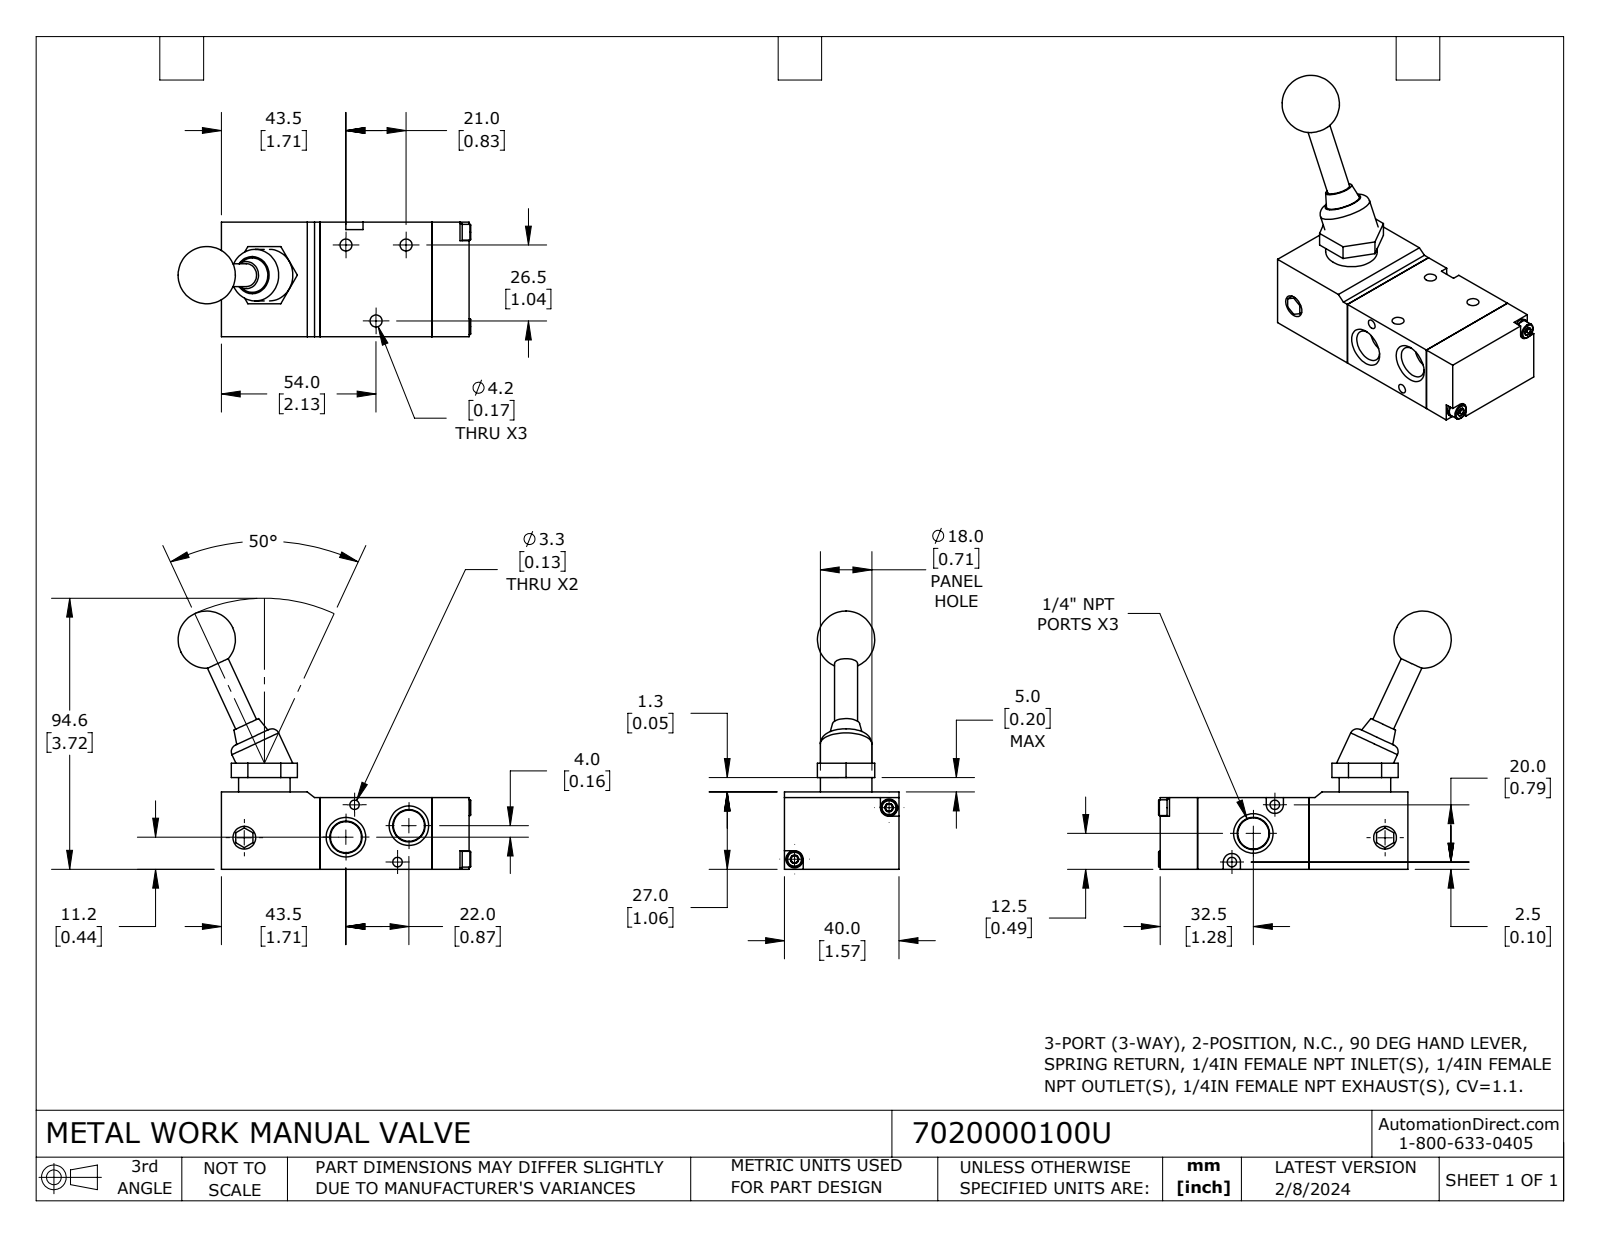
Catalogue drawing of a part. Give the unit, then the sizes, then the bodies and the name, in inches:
Units: inches
Overall size (bounding box): 4.024 × 3.549 × 1.575
Round holes (diameter × count): ⌀0.165 ×3, ⌀0.118 ×2, ⌀0.13 ×2, ⌀0.313 ×1
Round bosses / shafts (diameter × count): ⌀0.709 ×2, ⌀0.236 ×2, ⌀0.217 ×2, ⌀0.315 ×1
Partial cylindrical surfaces — rounded edges, fillets, slot ends (radius × count): R0.118 ×2
Main face-to-face distances: 0.984, 1.535, 1.575, 2.894, 1.358, 1.063, 0.079, 0.512, 2.047, 3.406
Hole centre spacings: 1.122, 0.827, 0.984, 1.48, 1.582, 2.133
Volume: 5.925 in³ · Surface area: 38.19 in²
Bodies: 8 solids, 183 faces (96 planar, 41 cylindrical, 46 other)
Part name (STEP PRODUCT): 7020000100U
STEP written by: SolidWorks 2023 (CONFIG_CONTROL_DESIGN)
